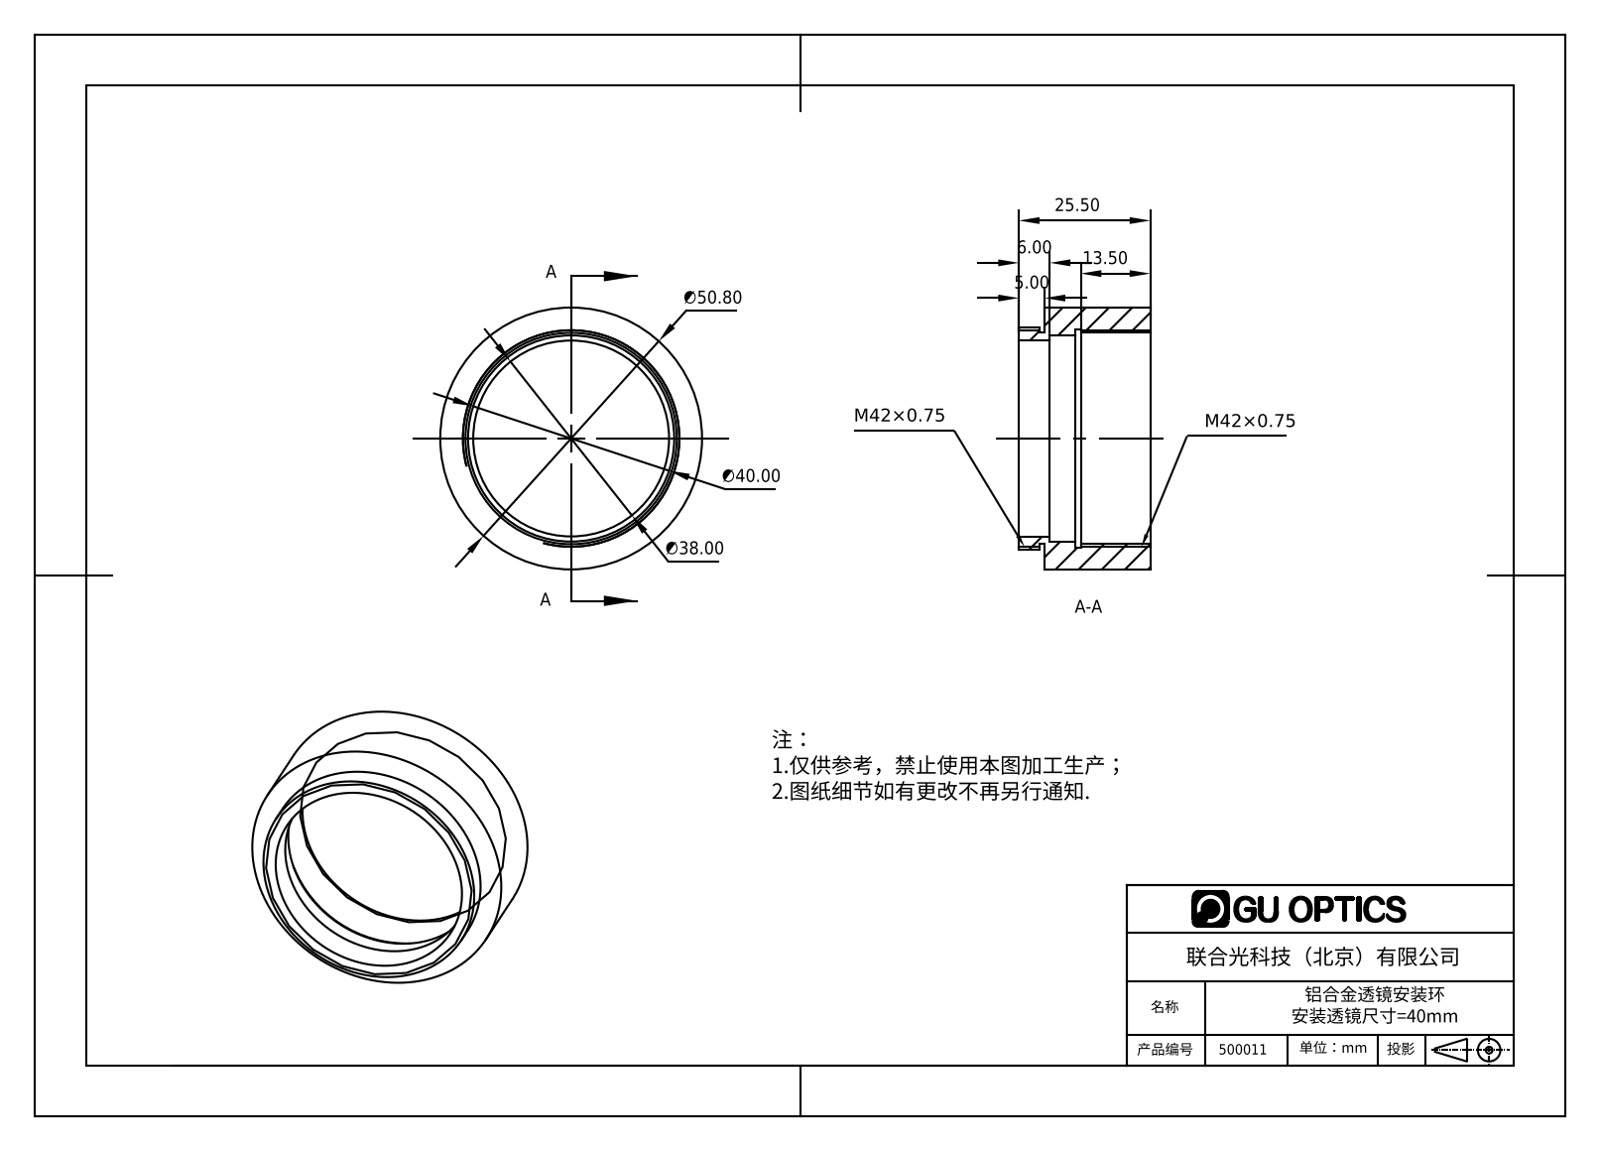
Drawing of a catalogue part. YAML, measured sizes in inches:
part_name: "500011"
step_written_by: "SolidWorks 2016 (AUTOMOTIVE_DESIGN)"
units: inches
bodies: {solids: 1, faces: 21, planar: 7, cylindrical: 14, other: 0}
overall_size: [2, 2, 1.004]
volume: 0.999
surface_area: 14.51
round_holes:
  - {diameter: 1.496, count: 1}
  - {diameter: 1.575, count: 1}
  - {diameter: 1.614, count: 1}
  - {diameter: 1.661, count: 1}
round_bosses_or_shafts:
  - {diameter: 2, count: 1}
  - {diameter: 1.693, count: 1}
face_to_face_distances: [0.807, 0.197, 0.236, 0.039, 1.004, 0.276, 0.433, 0.571, 0.157, 0.846]
